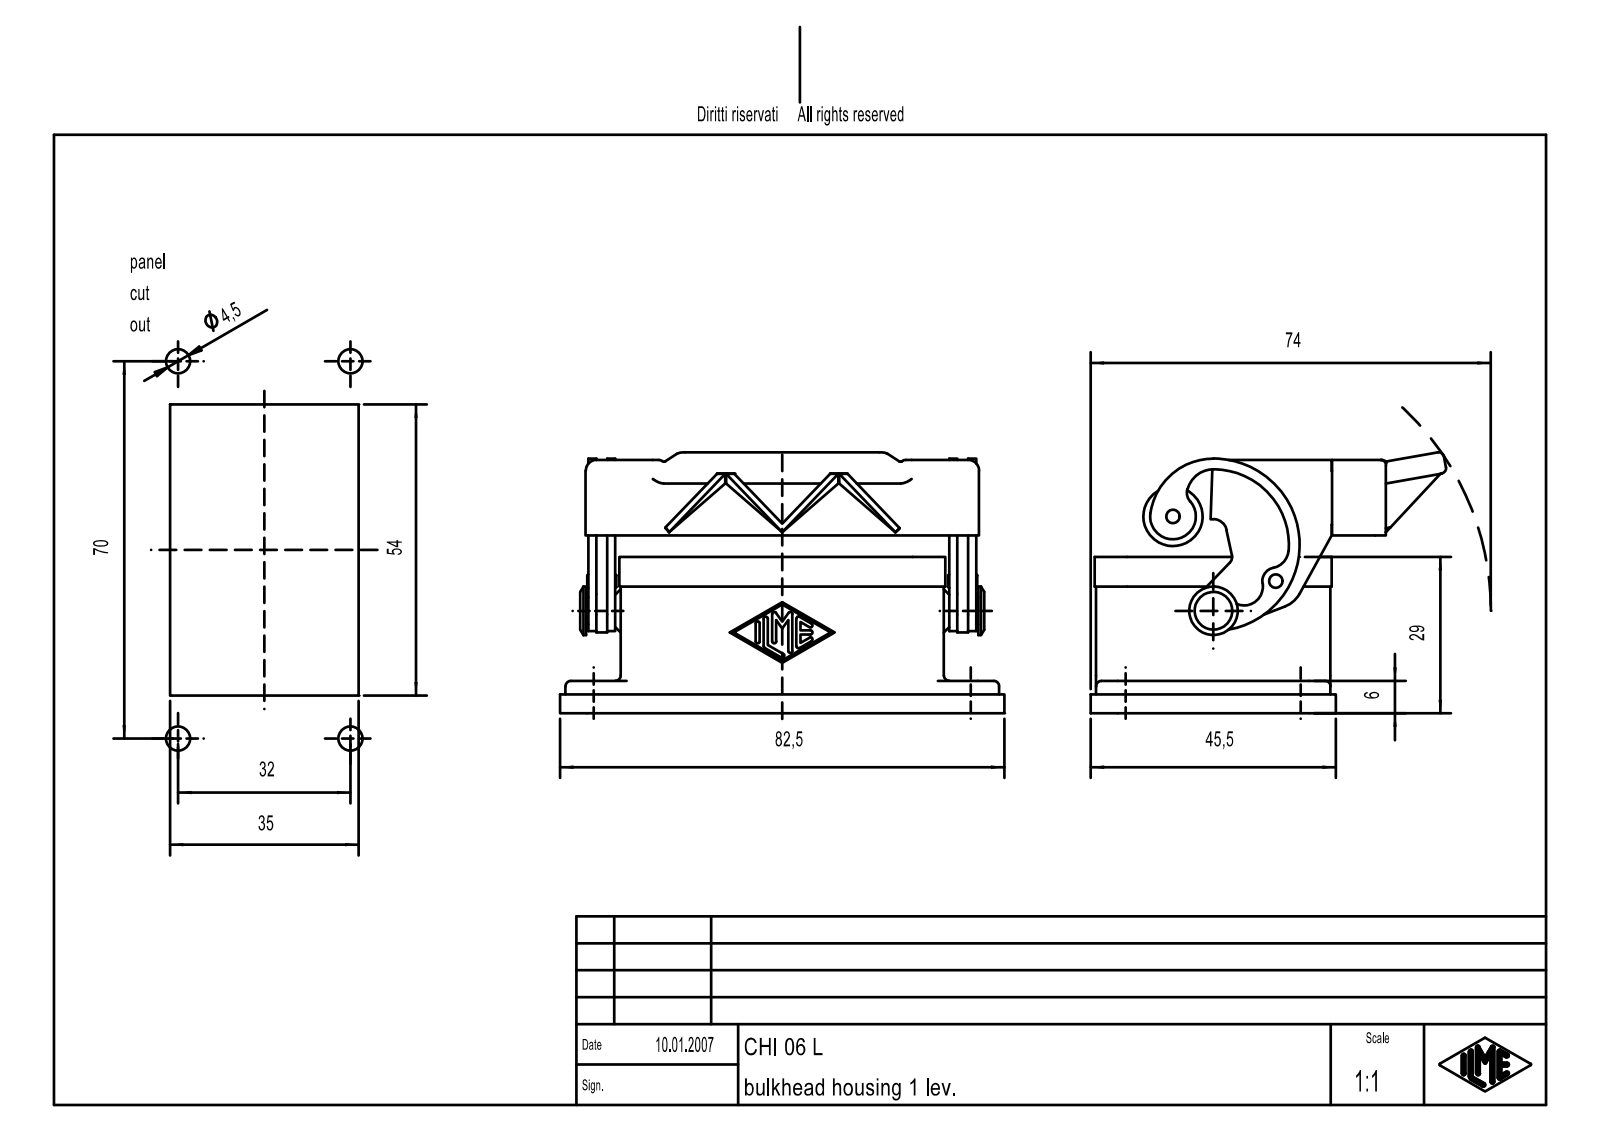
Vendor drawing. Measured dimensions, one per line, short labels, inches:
name: CHI_06_L
written by: PTC Creo Elements/Direct Modeling 19.0E 27-Jun-2016 (C) Parametric Technology GmbH (AUTOMOTIVE_DESIGN)
unit: in
bodies: 1 solid, 472 faces (212 planar, 200 cylindrical, 60 other)
size: 3.248 × 2.596 × 1.906
volume: 2.26 in³; area: 39.3 in²
holes: 4× ⌀0.097, 4× ⌀0.122, 4× ⌀0.173, 1× ⌀0.098
bosses: 1× ⌀0.433, 1× ⌀0.354, 1× ⌀0.197, 1× ⌀0.118, 1× ⌀0.079
rounds: 14× R0.015, 13× R0.039, 12× R0.079, 8× R0.236, 7× R0.098, 6× R0.197, 5× R0.059, 5× R0.157
face distances: 0.157, 0.118, 1.594, 0.039, 0.03, 2.638, 0.217, 0.098, 0.138, 0.236
hole spacings: 0.521, 1.269, 2.246, 2.527, 1.063, 1.26, 1.732, 2.032
